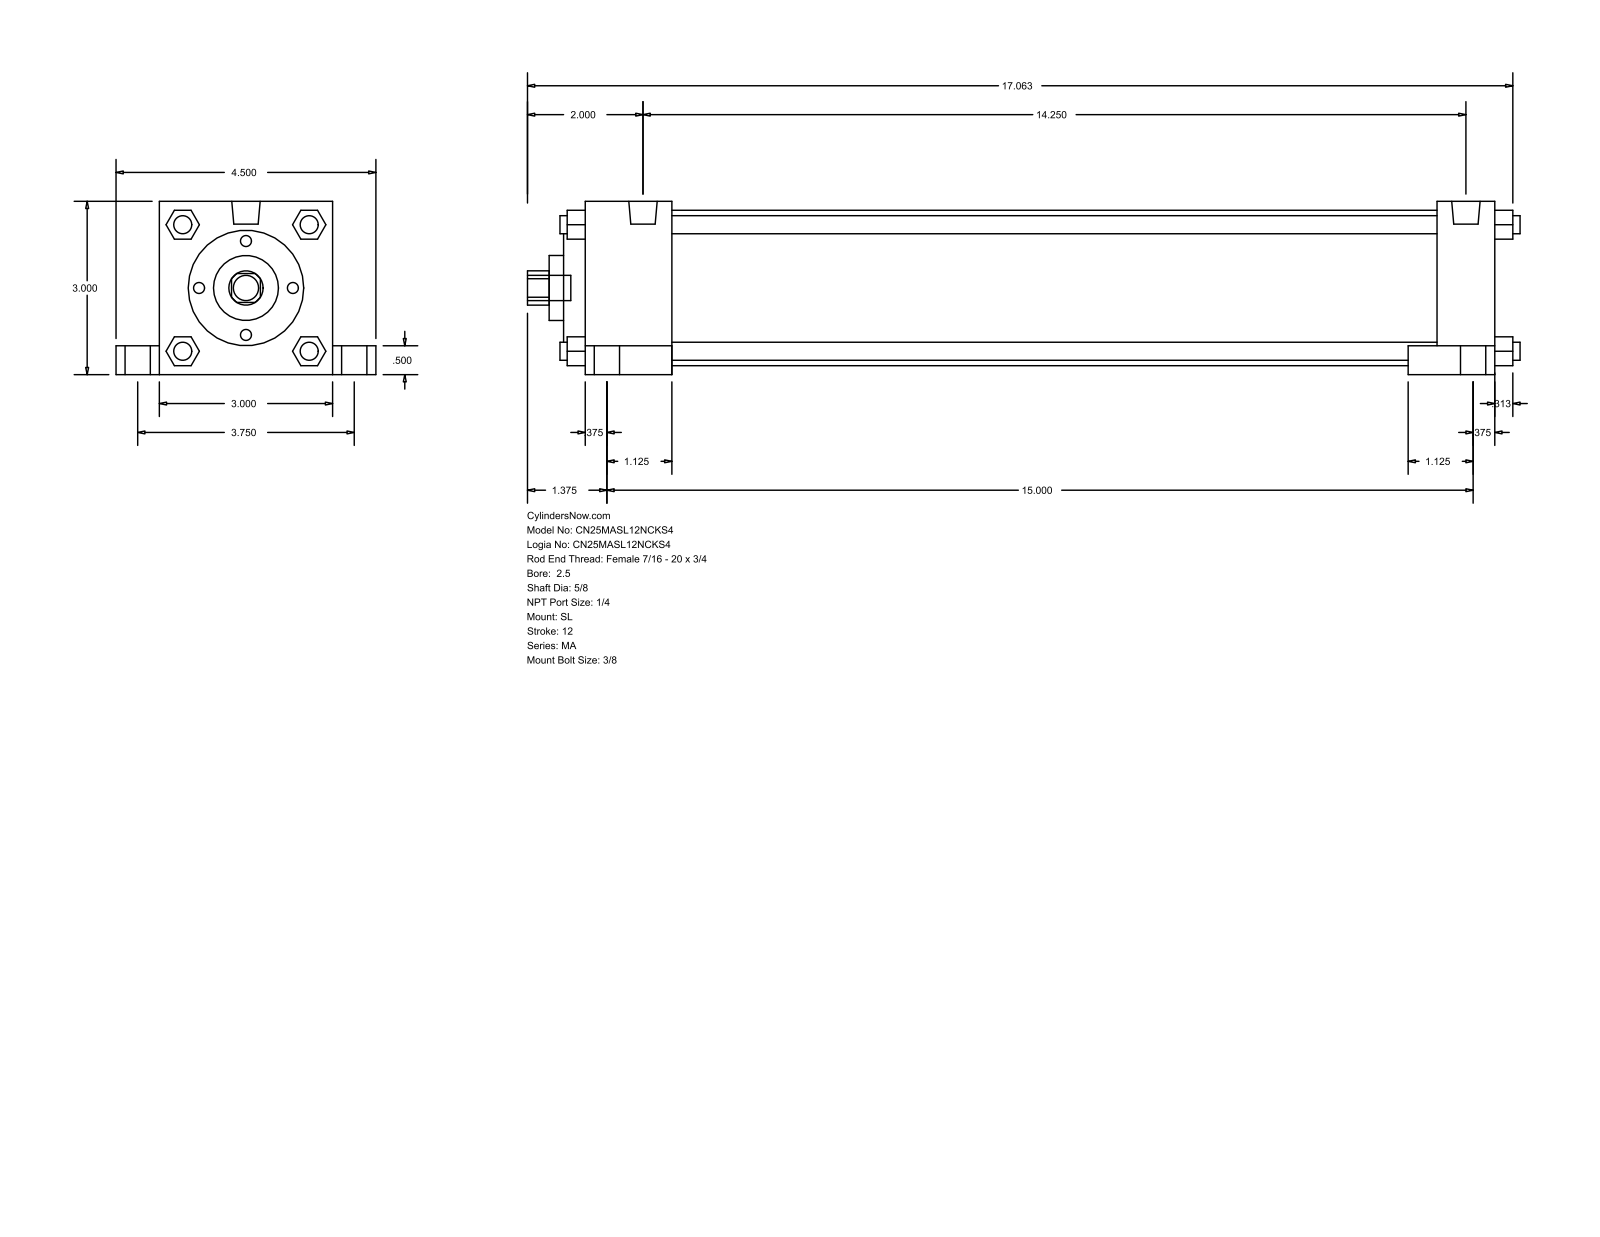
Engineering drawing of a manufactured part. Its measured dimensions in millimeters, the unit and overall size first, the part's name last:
Units: millimetres
Overall size (bounding box): 436.56 × 114.3 × 76.2
Round holes (diameter × count): ⌀15.88 ×1, ⌀28.57 ×1, ⌀50.8 ×1, ⌀68.33 ×1
Round bosses / shafts (diameter × count): ⌀7.94 ×8, ⌀11.11 ×5, ⌀17.46 ×4, ⌀12.49 ×2
Partial cylindrical surfaces — rounded edges, fillets, slot ends (radius × count): R7.54 ×1
Main face-to-face distances: 76.2, 400.05, 12.7, 336.55, 25.4, 38.1, 361.95, 374.65, 19.05, 63.5
Bodies: 0 solids, 150 faces (113 planar, 37 cylindrical, 0 other)
Part name (STEP PRODUCT): MA_SL__0250_0.625
STEP written by: GSSL Pune (CONFIG_CONTROL_DESIGN)
